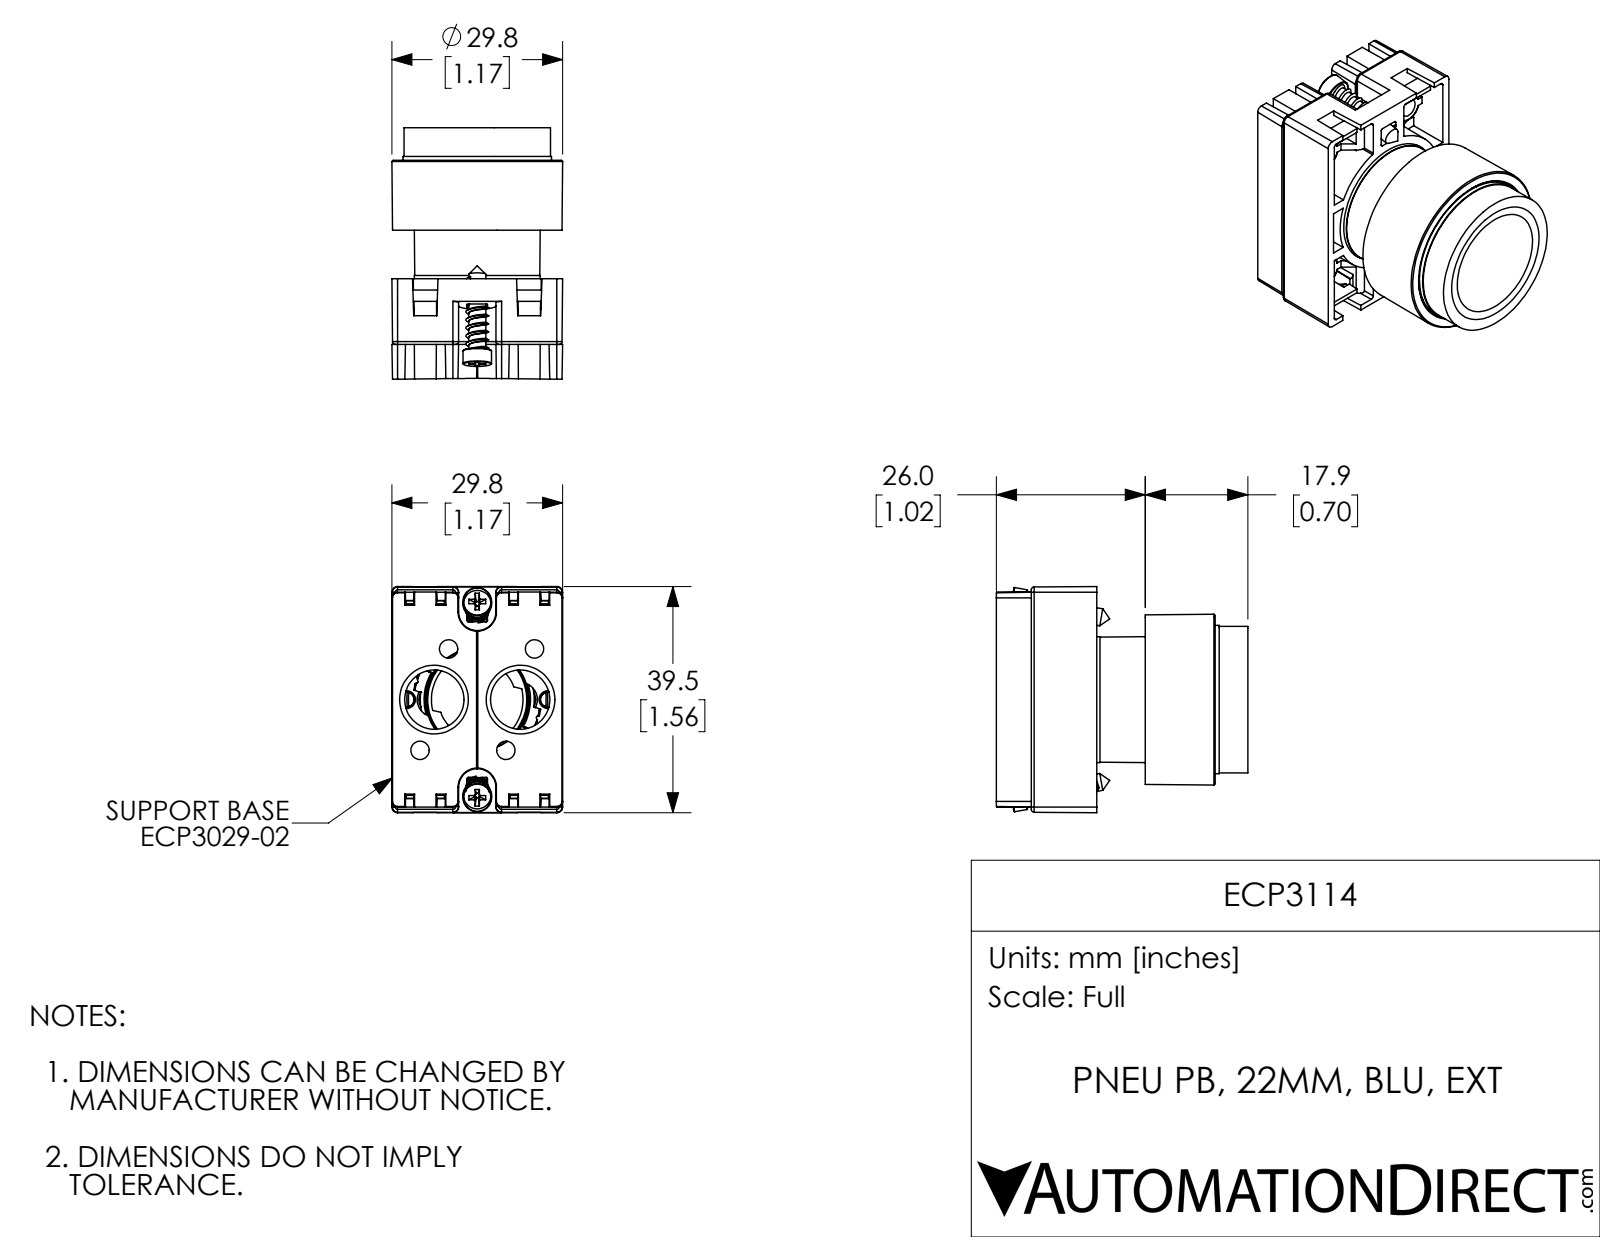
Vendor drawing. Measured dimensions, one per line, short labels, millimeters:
name: ECP3114
written by: SolidWorks 2017 (AUTOMOTIVE_DESIGN)
unit: mm
bodies: 7 solids, 781 faces (364 planar, 133 cylindrical, 284 other)
size: 43.9 × 39.5 × 29.8
volume: 16 800 mm³; area: 19 080 mm²
holes: 4× ⌀2.1, 2× ⌀10.3, 1× ⌀17.7, 1× ⌀18.6
bosses: 2× ⌀5, 2× ⌀3, 1× ⌀25.9, 1× ⌀25.6, 1× ⌀22
rounds: 18× R0.5, 8× R0.2, 8× R0.3, 4× R0.2, 4× R1, 2× R0.2, 2× R3, 2× R3.3
face distances: 32, 4.5, 1.7, 18.2, 24.4, 20.6, 11.5, 14.9, 13.4, 13.2
hole spacings: 7.7, 13.7, 20.8, 7.5, 12, 24.7, 27.5, 15
